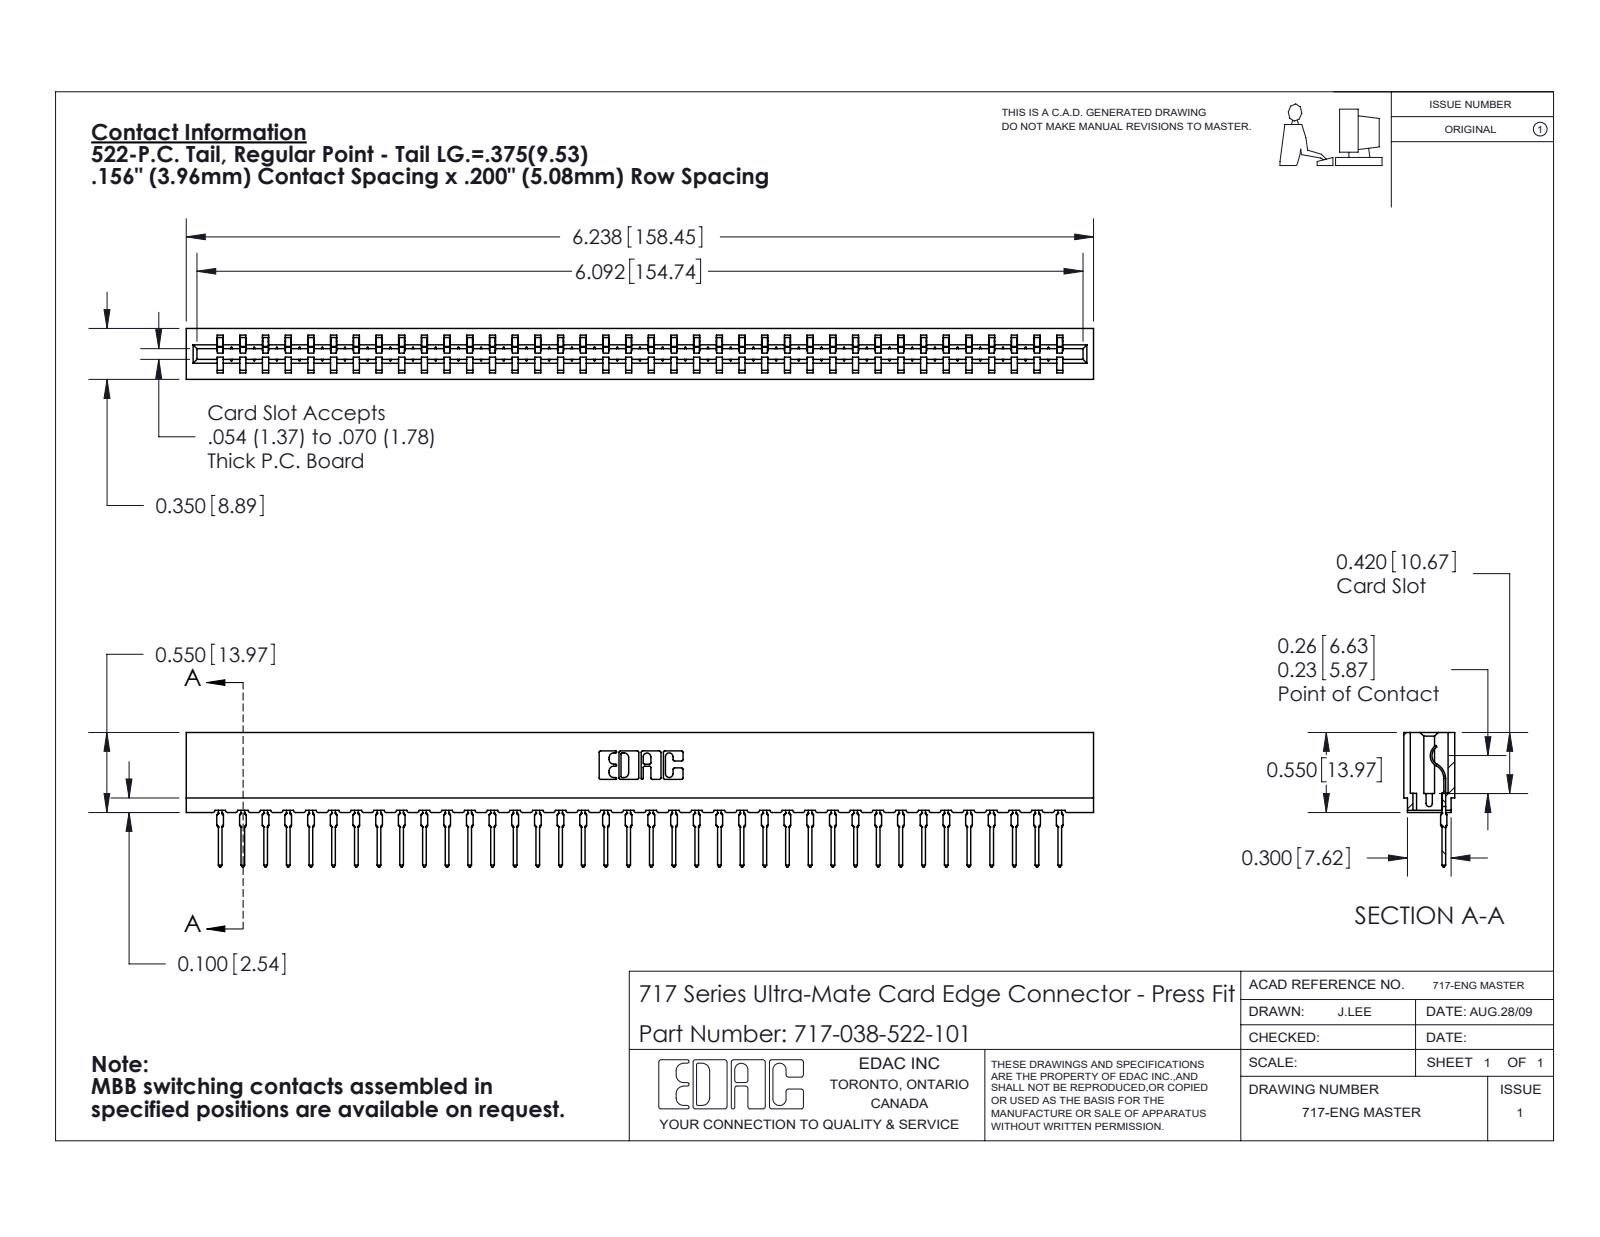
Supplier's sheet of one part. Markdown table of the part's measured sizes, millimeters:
| quantity | value |
| --- | --- |
| part name | 745-292-001_522; 717-038-522-101; 717 Part_Insulator Option - 06 |
| STEP written by | SolidWorks 2020 (CONFIG_CONTROL_DESIGN) |
| units | millimeters |
| bodies | 39 solids, 4388 faces (2638 planar, 762 cylindrical, 988 other) |
| overall size | 158.4 × 23.5 × 8.9 |
| volume | 13 400 mm³ |
| surface area | 18 880 mm² |
| partial cylindrical surfaces (radius × count) | 0.4 × 76, 0.5 × 76, 0.3 × 22, 0.2 × 6, 0.8 × 6, 0.1 × 4, 0.3 × 4, 0.7 × 3 |
| main face-to-face distances | 5.4, 3.5, 8.9, 1.9, 1.1, 7.7, 2.4, 4.2, 1.6, 7.3 |
